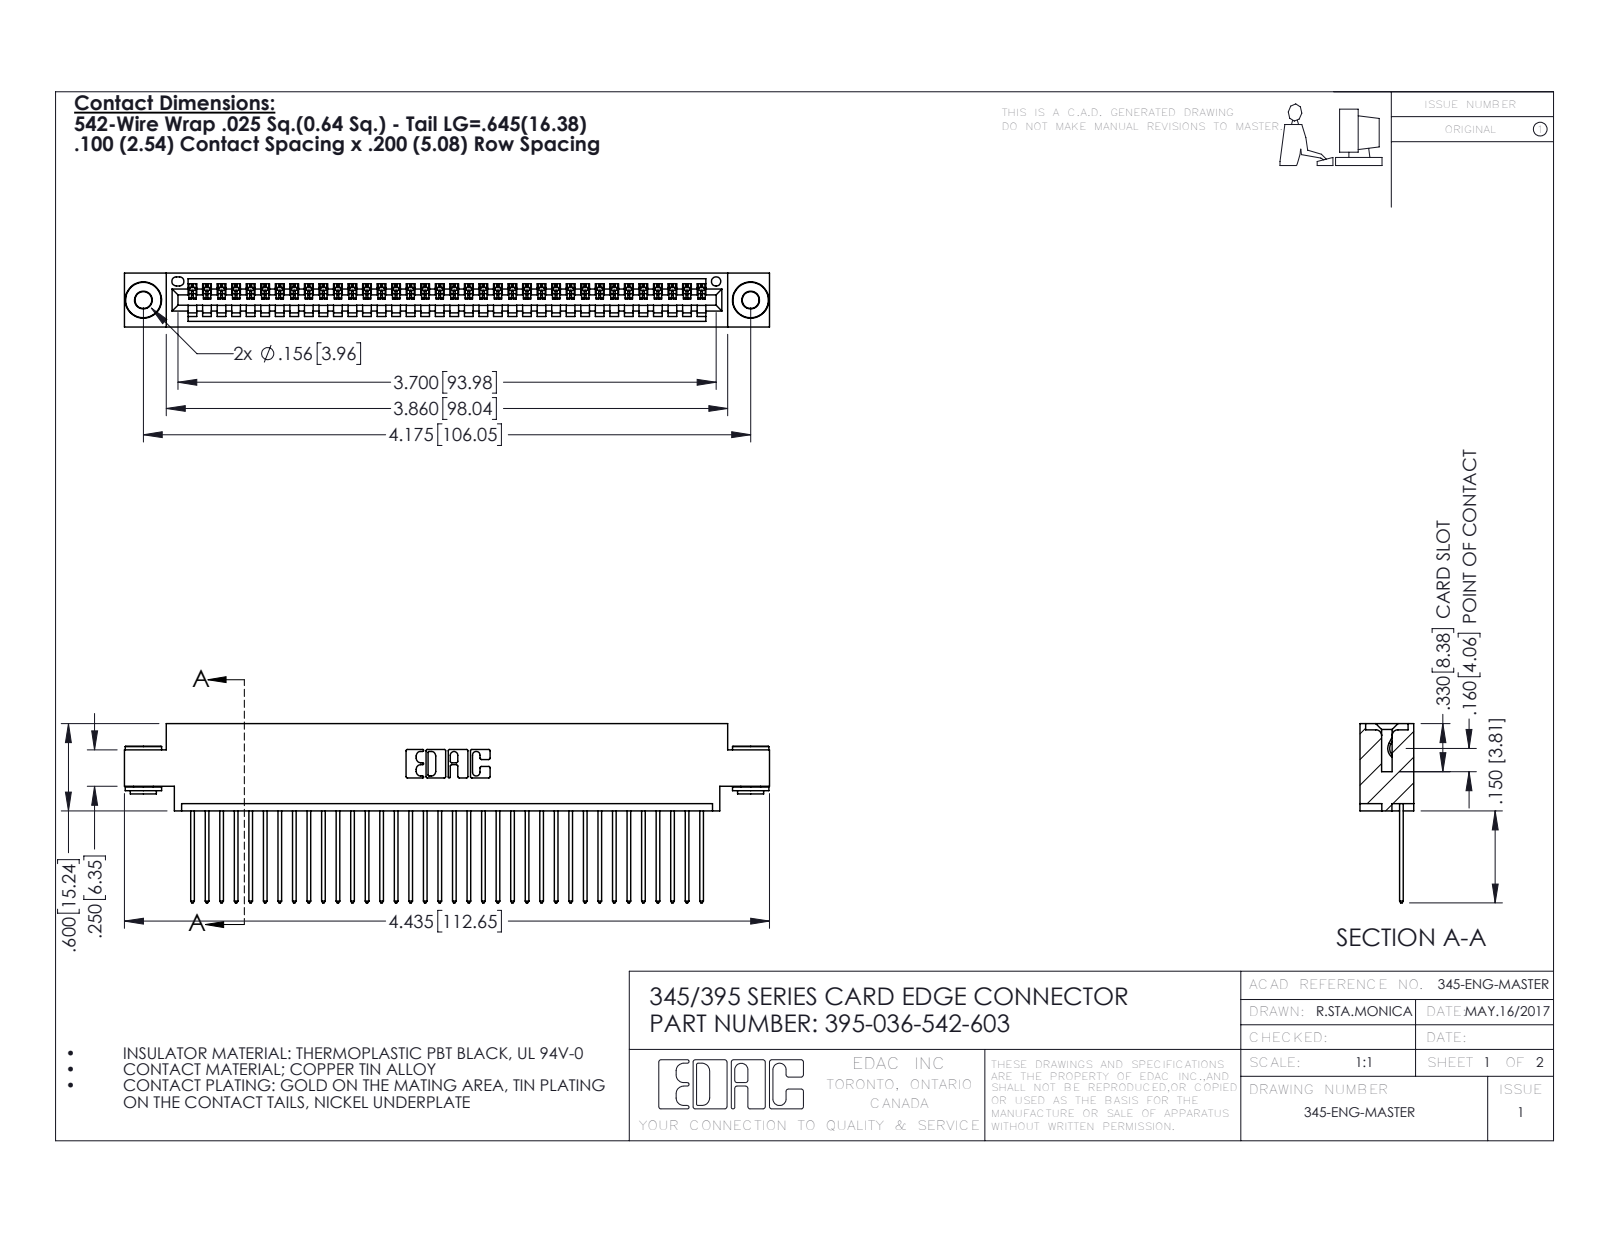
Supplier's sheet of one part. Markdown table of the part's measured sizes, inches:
| quantity | value |
| --- | --- |
| part name | 345-250-002_345-250-002-102; 345-292-001_345-293-142; 395-036-542-603; 345 Part_0.170 Offset - 0.156 Dia-TH |
| STEP written by | SolidWorks 2016 (CONFIG_CONTROL_DESIGN) |
| units | inches |
| bodies | 39 solids, 2256 faces (1534 planar, 714 cylindrical, 8 other) |
| overall size | 4.435 × 1.232 × 0.37 |
| volume | 0.649 in³ |
| surface area | 23.1 in² |
| round holes (diameter × count) | 0.116 × 2, 0.156 × 2, 0.064 × 1 |
| round bosses / shafts (diameter × count) | 0.25 × 2, 0.18 × 2, 0.136 × 2 |
| partial cylindrical surfaces (radius × count) | 0.006 × 72, 0.01 × 72, 0.01 × 22, 0.007 × 6, 0.031 × 6, 0.026 × 3, 0.031 × 2, 0.04 × 2 |
| main face-to-face distances | 0.072, 0.298, 0.37, 0.098, 0.272, 0.025, 0.2, 0.225, 0.175, 0.149 |
| hole center spacings | 0.27, 3.939, 4.175 |
